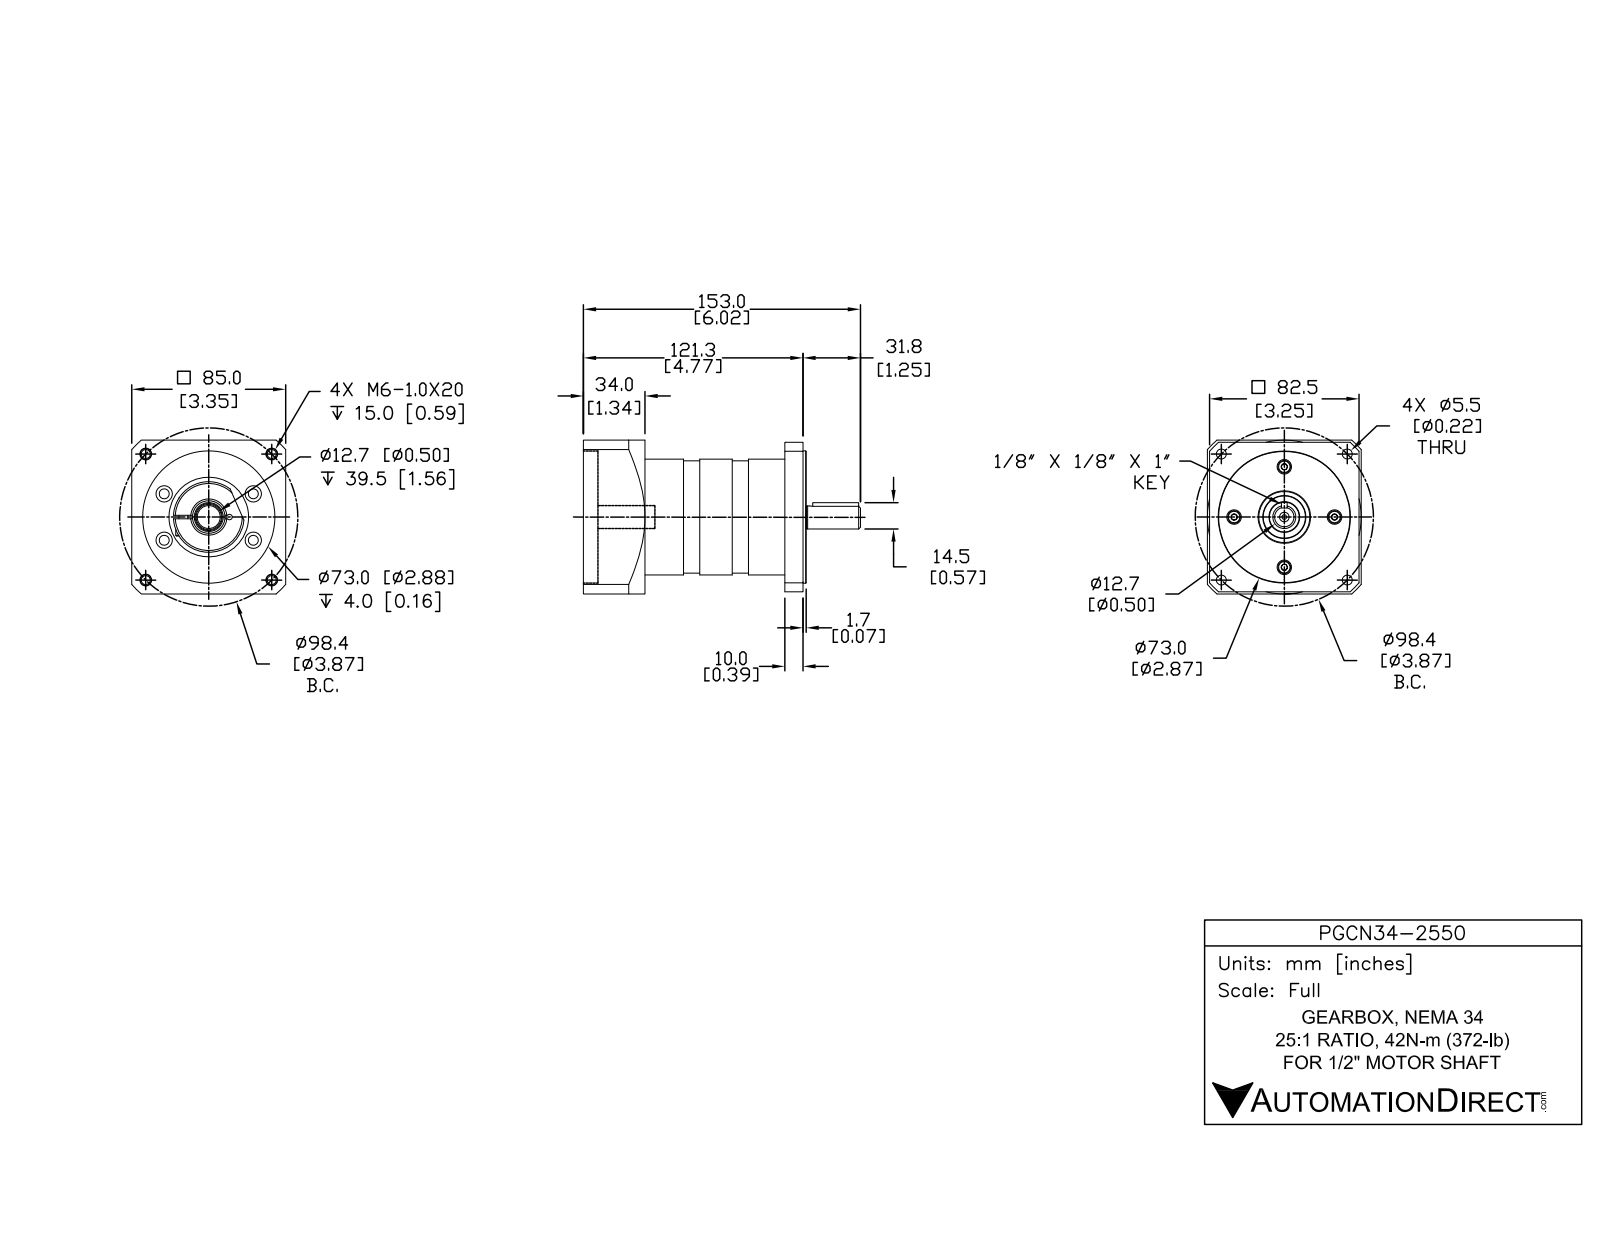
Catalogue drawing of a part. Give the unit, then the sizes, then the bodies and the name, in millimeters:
Units: millimetres
Overall size (bounding box): 153.1 × 85 × 85
Round holes (diameter × count): ⌀5 ×5, ⌀9 ×5, ⌀3.3 ×4, ⌀4 ×4, ⌀5.5 ×4, ⌀5.5 ×4, ⌀6 ×4, ⌀8 ×4, ⌀14 ×2, ⌀2.5 ×1, ⌀12.7 ×1, ⌀28.2 ×1
Round bosses / shafts (diameter × count): ⌀7 ×4, ⌀73 ×1, ⌀64 ×1, ⌀62 ×1, ⌀39 ×1, ⌀23.8 ×1, ⌀23.3 ×1, ⌀20 ×1
Partial cylindrical surfaces — rounded edges, fillets, slot ends (radius × count): R1.5 ×1, R1.6 ×1, R9 ×1, R55 ×1, R56.5 ×1
Main face-to-face distances: 85, 11.8, 123, 111.3, 10, 34, 87.3, 33, 78.3, 1.8
Hole centre spacings: 35.5, 71.6, 13.2, 24.2, 27.7, 27.8, 28.8, 39.2
Volume: 501 400 mm³ · Surface area: 75 610 mm²
Bodies: 3 solids, 368 faces (108 planar, 146 cylindrical, 114 other)
Part name (STEP PRODUCT): Bushing_.5x14x20.5; PE-N34-II 14mm Input; N34-A06; PGCN34-2550
STEP written by: SolidWorks 2014 (AUTOMOTIVE_DESIGN)
